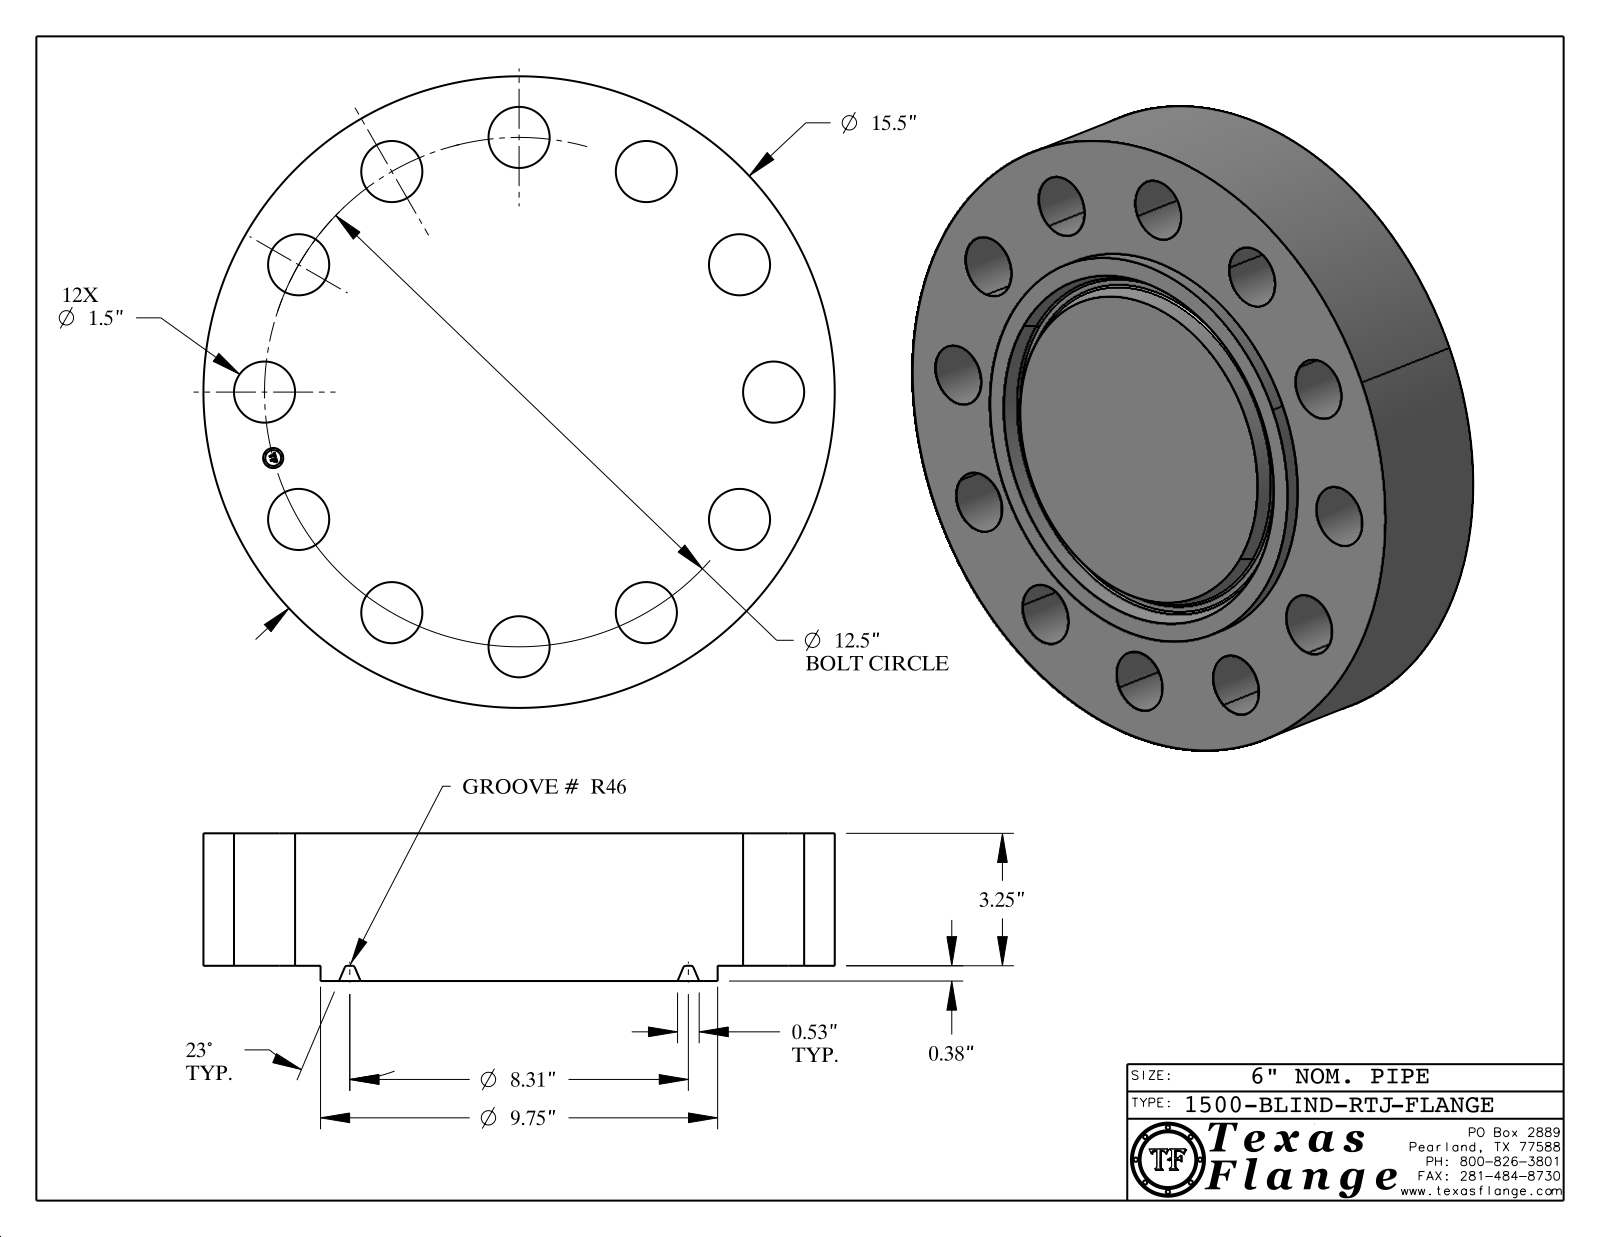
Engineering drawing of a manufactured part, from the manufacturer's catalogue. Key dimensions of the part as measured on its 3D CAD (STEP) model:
Part name (STEP PRODUCT): 1500-BLIND-RTJ
STEP written by: CATIA V5 STEP AP214 (AUTOMOTIVE_DESIGN)
Units: inches
Bodies: 1 solid, 426 faces (370 planar, 48 cylindrical, 8 other)
Overall size (bounding box): 15.5 × 15.5 × 3.625
Volume: 568.7 in³ · Surface area: 701 in²
Round holes (diameter × count): ⌀1.5 ×12, ⌀0.495 ×1
Round bosses / shafts (diameter × count): ⌀0.03 ×8, ⌀15.5 ×1, ⌀9.75 ×1, ⌀0.39 ×1
Main face-to-face distances: 3.25, 0.375, 3.625, 3.61, 3.235, 0.015, 0.148, 0.144, 0.027, 0.096
Hole centre spacings: 8.839, 3.235, 6.25, 10.826, 12.074, 12.5, 3.235, 6.25
